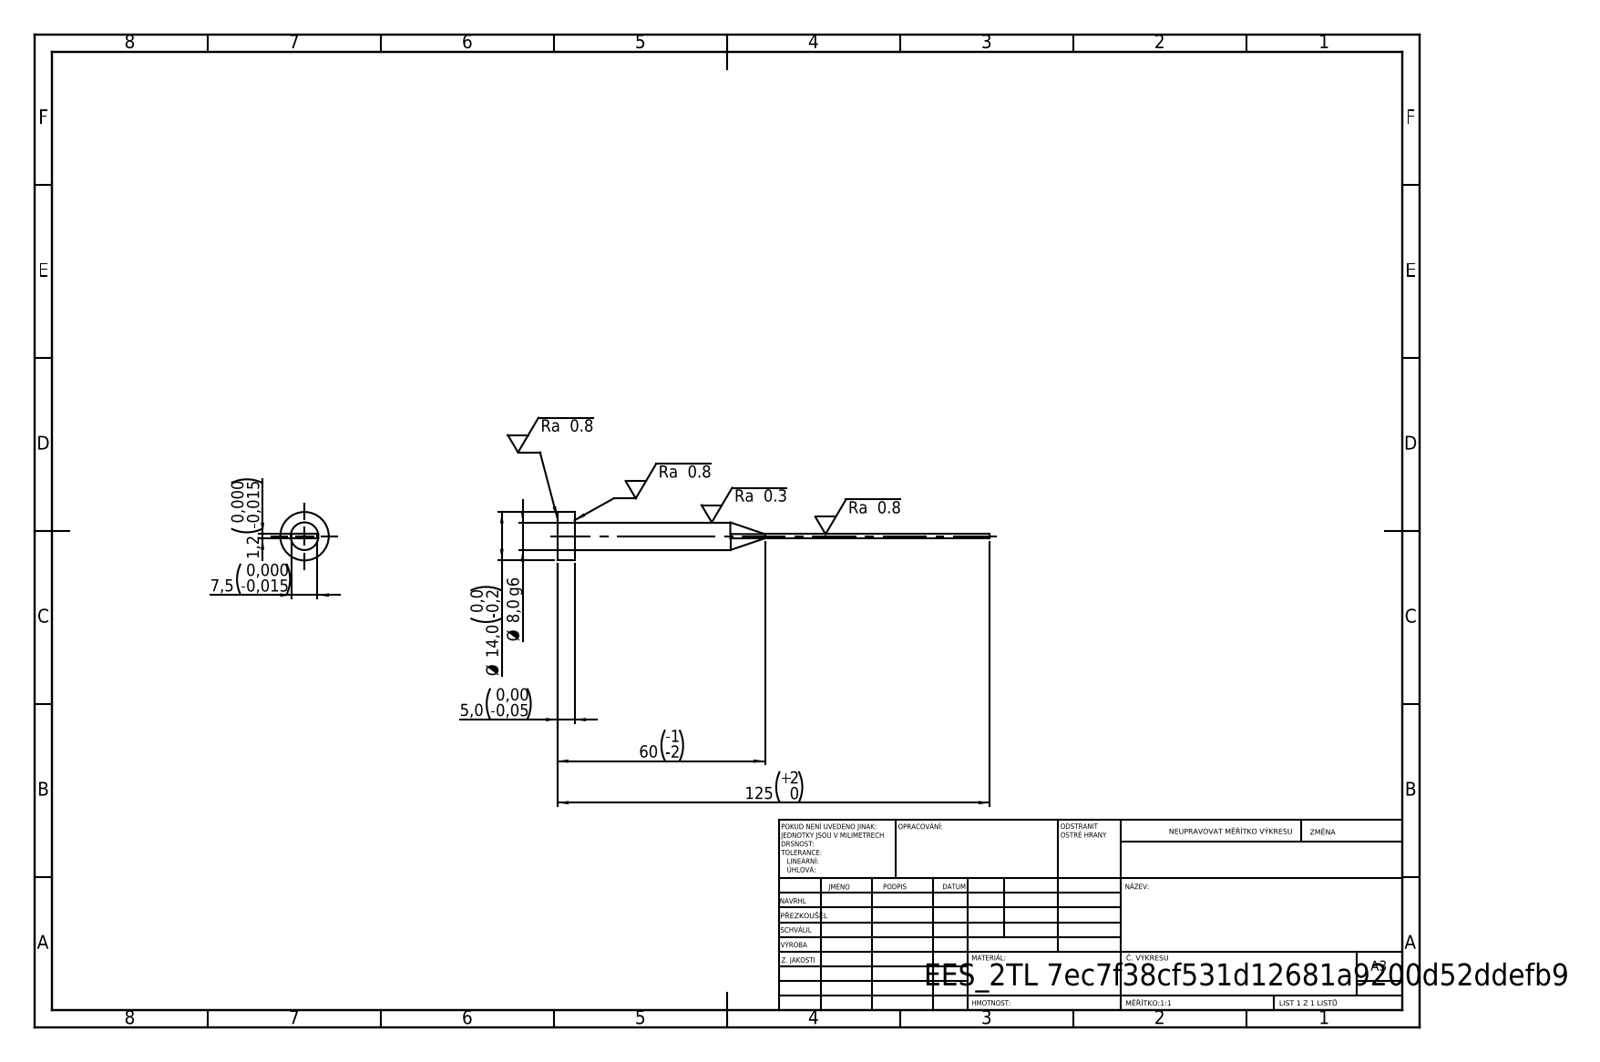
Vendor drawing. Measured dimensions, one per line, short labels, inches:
written by: SolidWorks 2019 (CONFIG_CONTROL_DESIGN)
unit: in
bodies: 1 solid, 15 faces (7 planar, 4 cylindrical, 4 other)
size: 4.921 × 0.551 × 0.551
volume: 0.238 in³; area: 4.582 in²
bosses: 1× ⌀0.551, 1× ⌀0.315
face distances: 0.047, 0.197, 0.295, 4.921, 4.724
